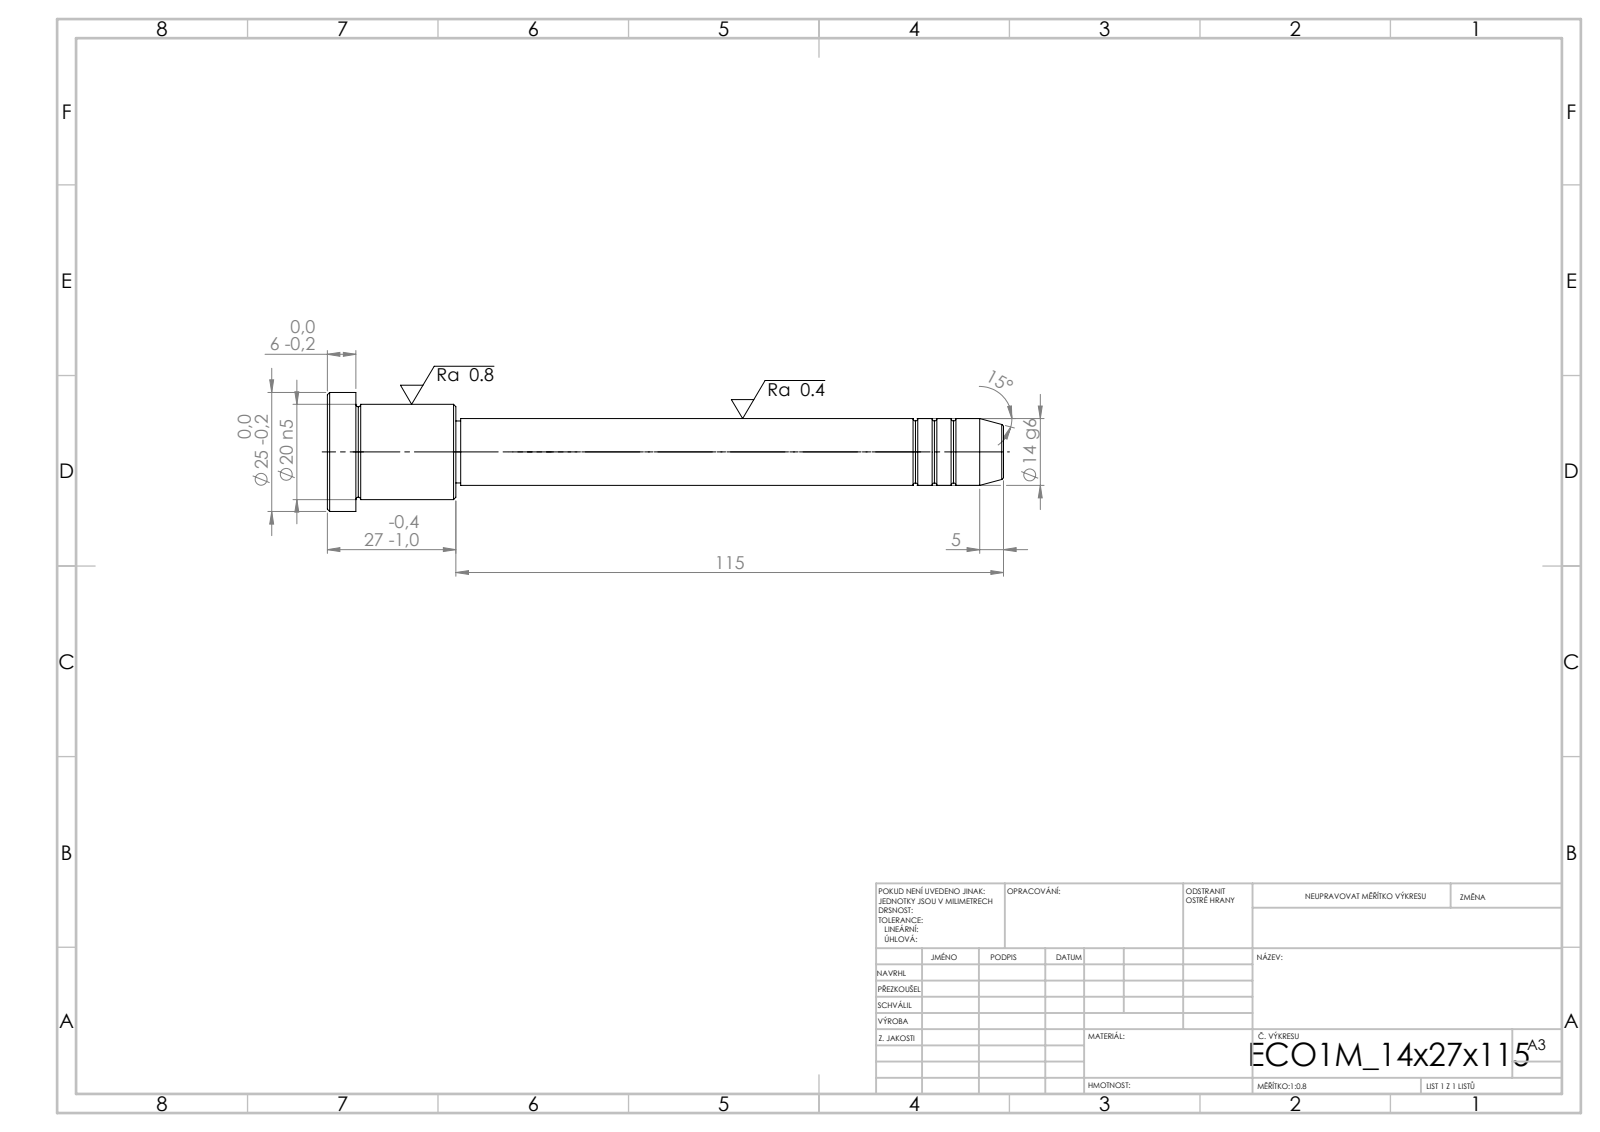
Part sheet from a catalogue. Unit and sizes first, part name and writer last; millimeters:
Units: millimetres
Overall size (bounding box): 142 × 25 × 25
Round bosses / shafts (diameter × count): ⌀25 ×1, ⌀20 ×1, ⌀14 ×1, ⌀13 ×1
Main face-to-face distances: 6, 21, 27, 115, 136, 142, 114, 1, 22, 28
Volume: 26 994 mm³ · Surface area: 7 855 mm²
Bodies: 1 solid, 43 faces (5 planar, 14 cylindrical, 24 other)
STEP written by: SolidWorks 2019 (CONFIG_CONTROL_DESIGN)
